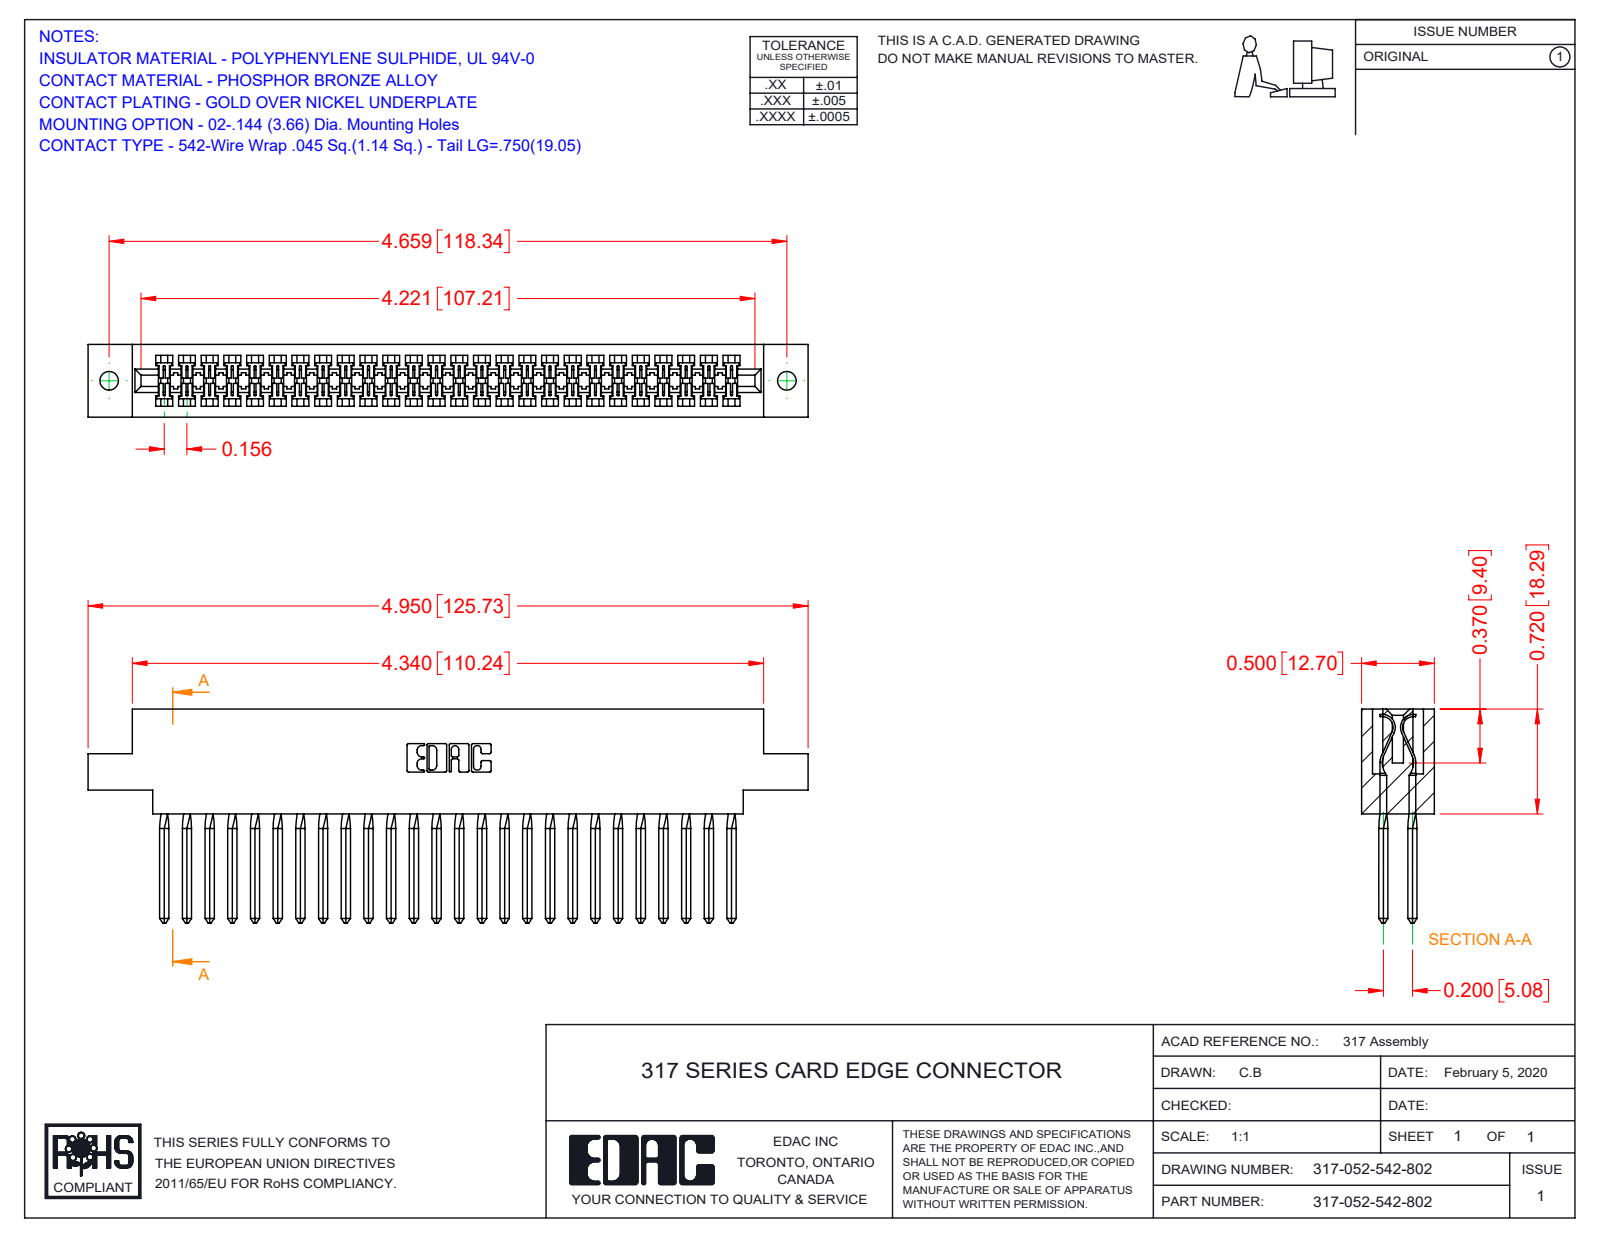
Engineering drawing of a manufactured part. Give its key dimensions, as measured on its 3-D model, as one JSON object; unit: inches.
{"part_name": "317-290-003_542; 317 Part_.144 Dia; 317-052-542-802", "step_written_by": "SolidWorks 2016 (CONFIG_CONTROL_DESIGN)", "units": "inches", "bodies": {"solids": 53, "faces": 3066, "planar": 2450, "cylindrical": 408, "other": 208}, "overall_size": [4.95, 1.47, 0.5], "volume_in3": 1.223, "surface_area_in2": 42, "round_holes": [[0.128, 2]], "partial_cylinders_radius": [[0.006, 104], [0.01, 22], [0.007, 6], [0.031, 6], [0.026, 3], [0.074, 2], [0.089, 2], [0.1, 2]], "face_to_face_distances": [0.5, 0.075, 0.425, 0.35, 0.2, 0.11, 0.116, 0.046, 0.72, 0.136], "hole_center_spacings": [4.659]}
